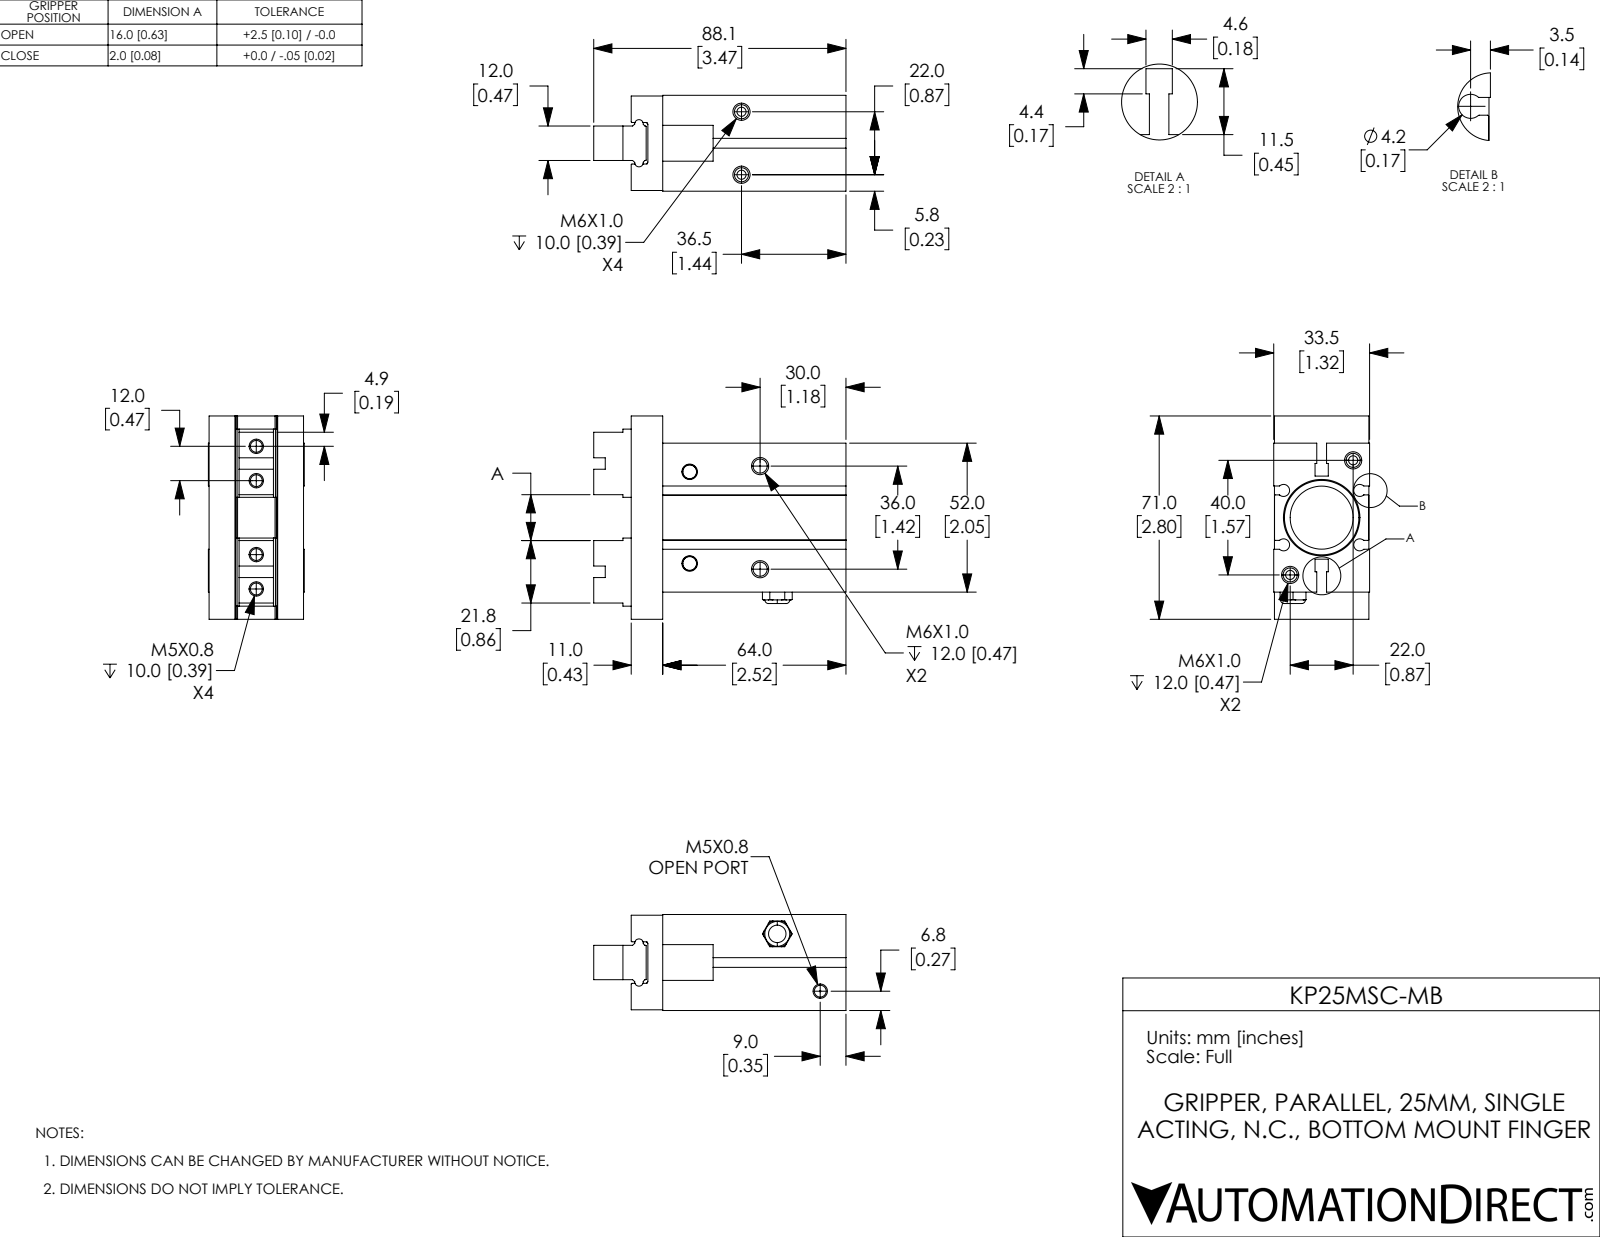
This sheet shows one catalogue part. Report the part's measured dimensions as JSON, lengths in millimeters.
{"part_name": "KP25MSC-MB; KP25MSC-MB-1; KP25MSC-MB-3; KP25MSC-MB-2", "step_written_by": "SolidWorks 2017 (CONFIG_CONTROL_DESIGN)", "units": "millimeters", "bodies": {"solids": 3, "faces": 265, "planar": 137, "cylindrical": 66, "other": 62}, "overall_size": [88.1, 71, 33.5], "volume_mm3": 115913, "surface_area_mm2": 32846, "round_holes": [[4.13, 6], [4.92, 4], [0.5, 2], [4.92, 2], [6.02, 2], [6.1, 1], [22, 1], [26, 1]], "partial_cylinders_radius": [[0.2, 8], [2.1, 4], [0.5, 2], [1.5, 2]], "face_to_face_distances": [10.5, 22.75, 33.2, 10.2, 23, 22.7, 33.5, 52, 33.25, 10.25], "hole_center_spacings": [12, 12.04, 12.9, 13.09, 22.83, 24.9, 34.69, 37.8]}
